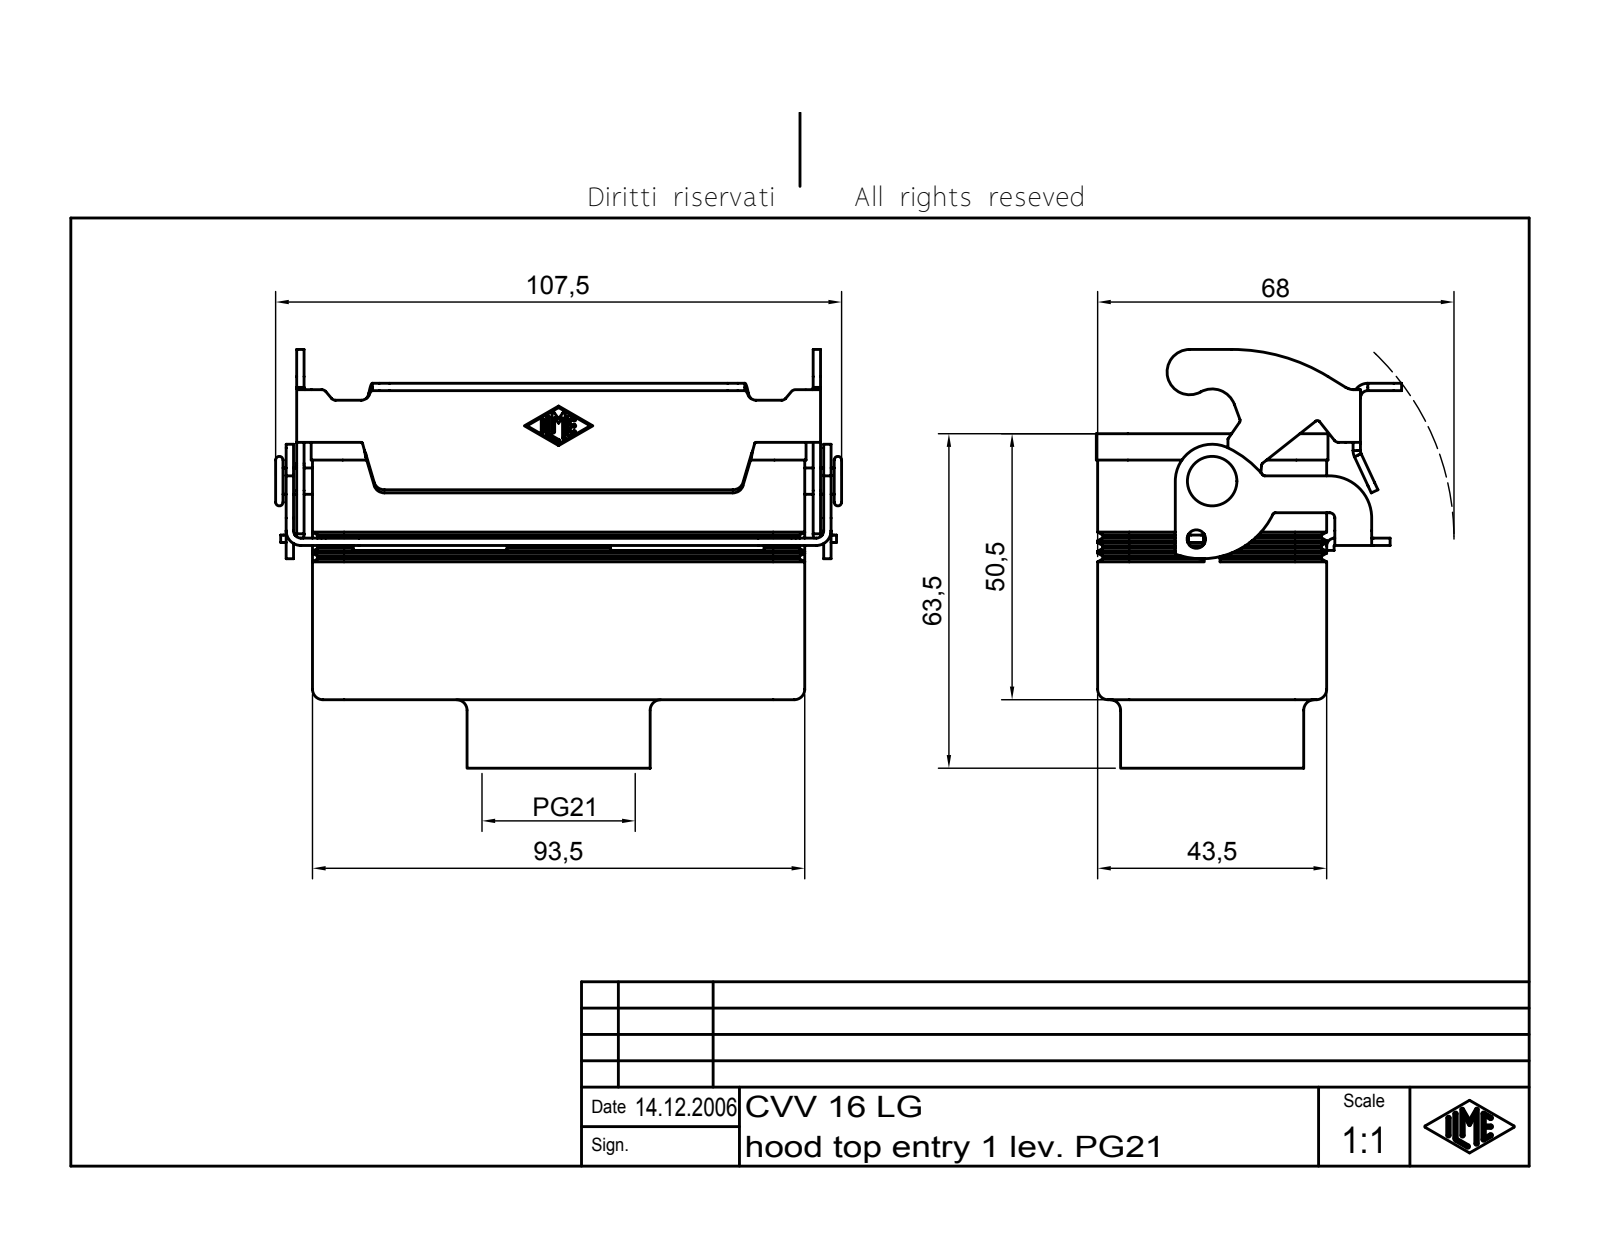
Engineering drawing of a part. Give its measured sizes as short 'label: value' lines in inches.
name: CVV 16 LG
written by: Autodesk Inventor 7 (AUTOMOTIVE_DESIGN)
unit: in
bodies: 2 solids, 494 faces (155 planar, 127 cylindrical, 212 other)
size: 4.232 × 3.13 × 2.283
volume: 4.283 in³; area: 75.91 in²
holes: 1× ⌀0.138, 1× ⌀0.936, 1× ⌀1.054
bosses: 1× ⌀1.369, 1× ⌀0.197, 1× ⌀0.126
rounds: 15× R0.01, 10× R0.079, 9× R0.02, 9× R0.059, 8× R0.039, 8× R0.236, 6× R0.055, 6× R0.11
face distances: 0.118, 1.594, 1.713, 1.476, 0.055, 3.563, 3.681, 0.463, 0.315, 0.157
